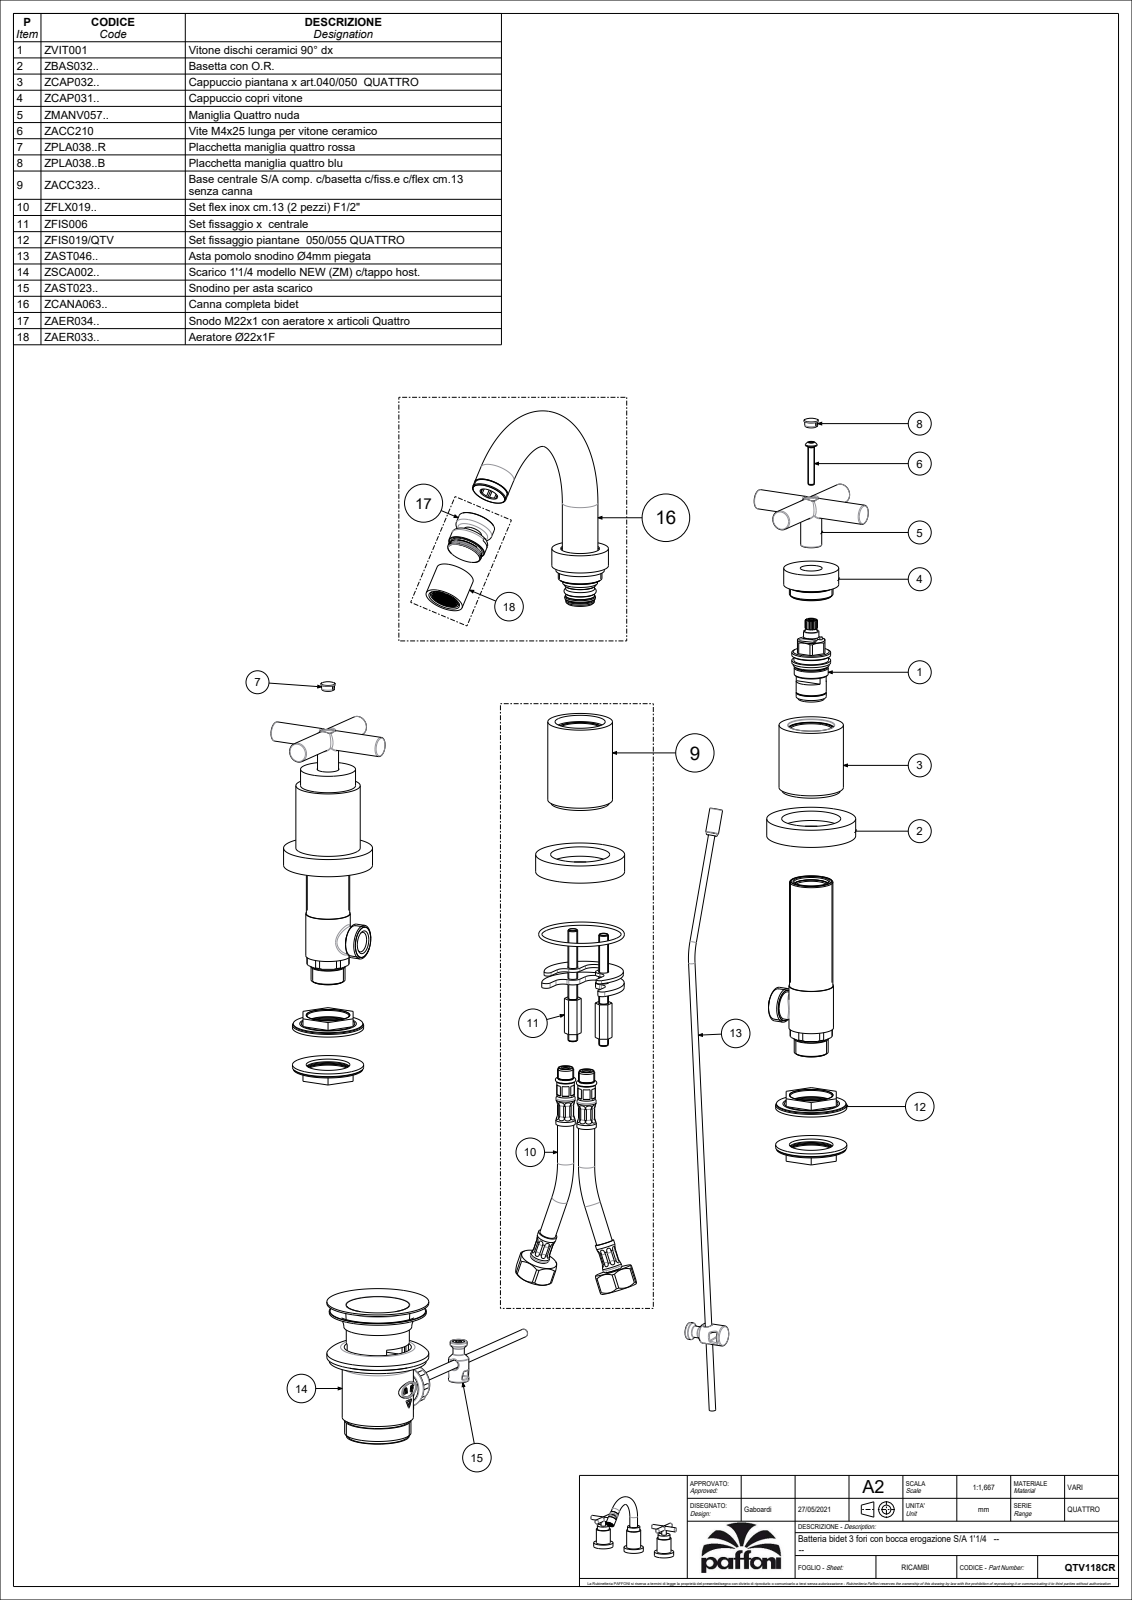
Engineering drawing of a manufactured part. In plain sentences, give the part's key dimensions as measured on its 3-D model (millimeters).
The part is named "QTV118CR". Its 3-D file was written by "CREO PARAMETRIC BY PTC INC, 2020044 (CONFIG_CONTROL_DESIGN)". It is 12 solids with 2593 faces: 1975 planar, 360 cylindrical and 258 other. Overall it measures 275 by 184.68 by 172.12 millimeters. Its volume is 290 060 cubic millimeters and its surface area 126 047 square millimeters. Round holes: 5 of diameter 19, 4 of diameter 4.5, 3 of diameter 7, 3 of diameter 25.5, 3 of diameter 36.5, 3 of diameter 47, 3 of diameter 53, 2 of diameter 3.3, 2 of diameter 5.25, 2 of diameter 8, 2 of diameter 8.8, 2 of diameter 9. Round bosses or shafts: 3 of diameter 55, 3 of diameter 49, 3 of diameter 36, 3 of diameter 24, 3 of diameter 12, 2 of diameter 39.8, 2 of diameter 34, 2 of diameter 26.8. Partial cylindrical surfaces (rounded edges, fillets, slot ends): 34 of radius 0.1, 4 of radius 0.5, 4 of radius 1, 2 of radius 3, 2 of radius 9.4, 1 of radius 4.25. The main face-to-face distances are 11, 5, 6, 4, 9, 10.5, 2, 56.5, 50.5, 61.5. The hole center spacings are 9.01, 14.87, 15.4, 23.82, 89.56, 92.64, 100, 107.62.
